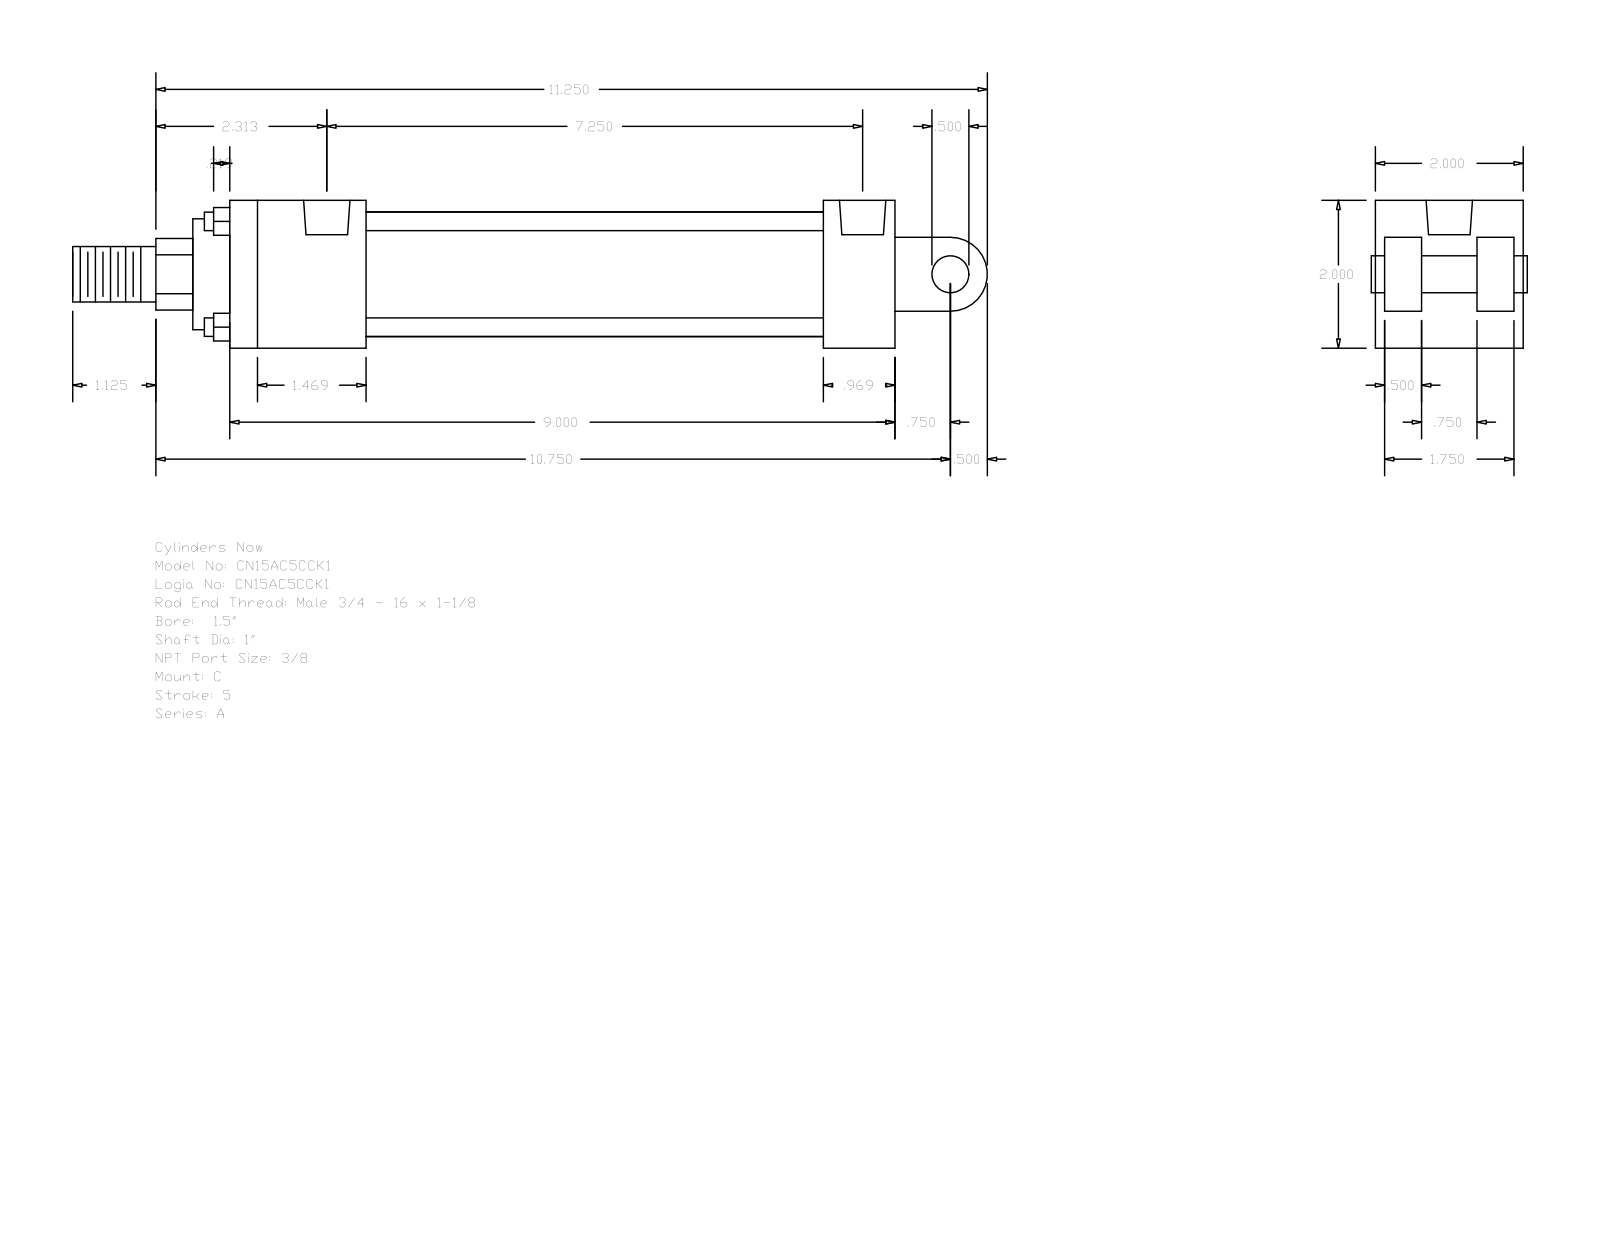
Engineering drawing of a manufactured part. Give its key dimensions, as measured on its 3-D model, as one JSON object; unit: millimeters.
{"part_name": "A_C__0150_1", "step_written_by": "GSSL Pune (CONFIG_CONTROL_DESIGN)", "units": "millimeters", "bodies": {"solids": 0, "faces": 99, "planar": 70, "cylindrical": 29, "other": 0}, "overall_size": [314.32, 50.8, 50.8], "round_holes": [[5.56, 4], [15.93, 2]], "round_bosses_or_shafts": [[6.35, 4], [42.93, 1], [38.1, 1], [25.4, 1], [19.05, 1], [12.7, 1]], "partial_cylinders_radius": [[12.29, 1], [12.7, 1]], "face_to_face_distances": [50.8, 12.7, 3.17, 15.87, 34.93, 47.63, 31.76, 228.6, 38.1, 203.99], "hole_center_spacings": [3.97, 176.21, 180.18, 184.15]}
